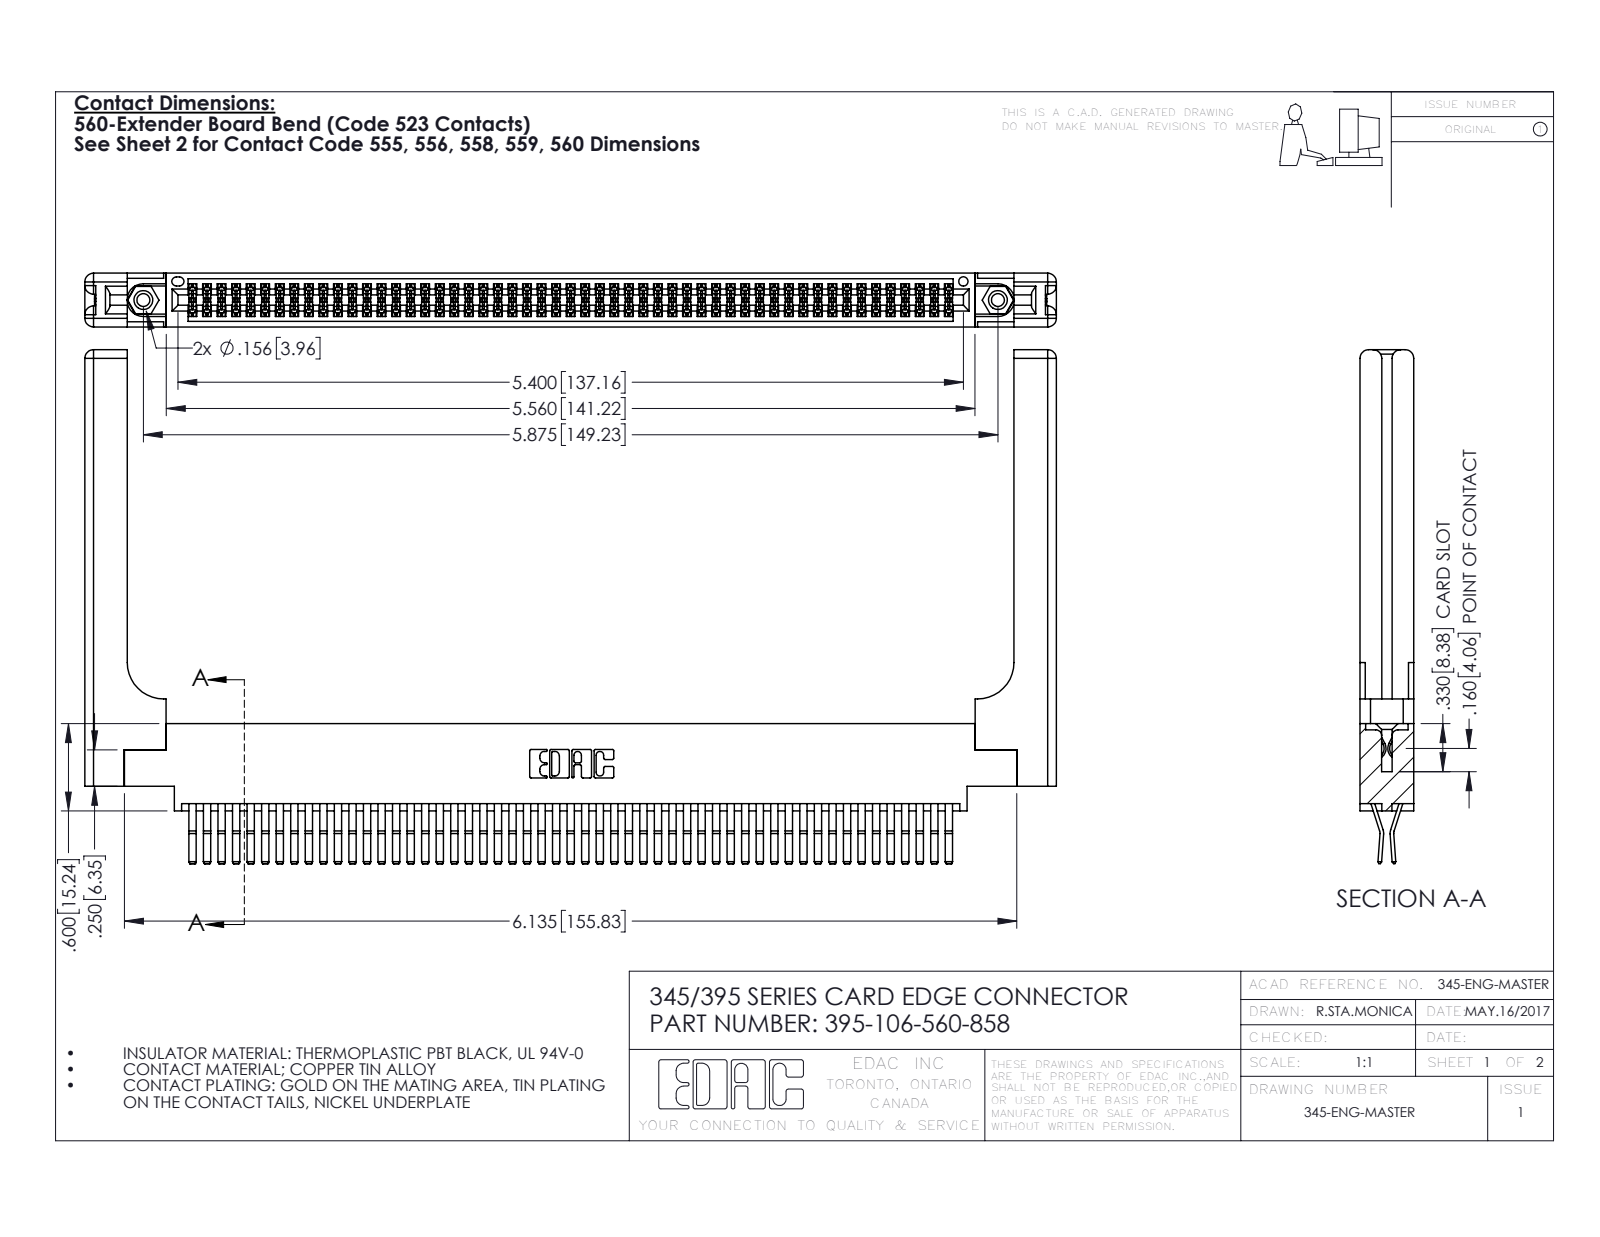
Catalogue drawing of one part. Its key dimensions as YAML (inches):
part_name: "345-292-001_560 Tail; 345 Part_0.170 Offset - 0.156 Dia-TH; 345-220-058_345-220-058; 345-250-001_345-250-001-102 (+1 more)"
step_written_by: "SolidWorks 2016 (CONFIG_CONTROL_DESIGN)"
units: inches
bodies: {solids: 111, faces: 5898, planar: 3730, cylindrical: 2108, other: 60}
overall_size: [6.679, 3.532, 0.37]
volume: 1.565
surface_area: 50.49
round_holes:
  - {diameter: 0.089, count: 2}
  - {diameter: 0.125, count: 2}
  - {diameter: 0.156, count: 2}
  - {diameter: 0.064, count: 1}
round_bosses_or_shafts:
  - {diameter: 0.155, count: 2}
partial_cylinders:
  - {radius: 0.006, count: 160}
  - {radius: 0.01, count: 22}
  - {radius: 0.06, count: 16}
  - {radius: 0.007, count: 6}
  - {radius: 0.031, count: 6}
  - {radius: 0.026, count: 3}
  - {radius: 0.01, count: 2}
  - {radius: 0.014, count: 2}
face_to_face_distances: [0.072, 0.37, 0.298, 0.025, 0.098, 0.272, 0.2, 0.225, 0.175, 0.148]
hole_center_spacings: [0.27, 5.639, 5.875]
